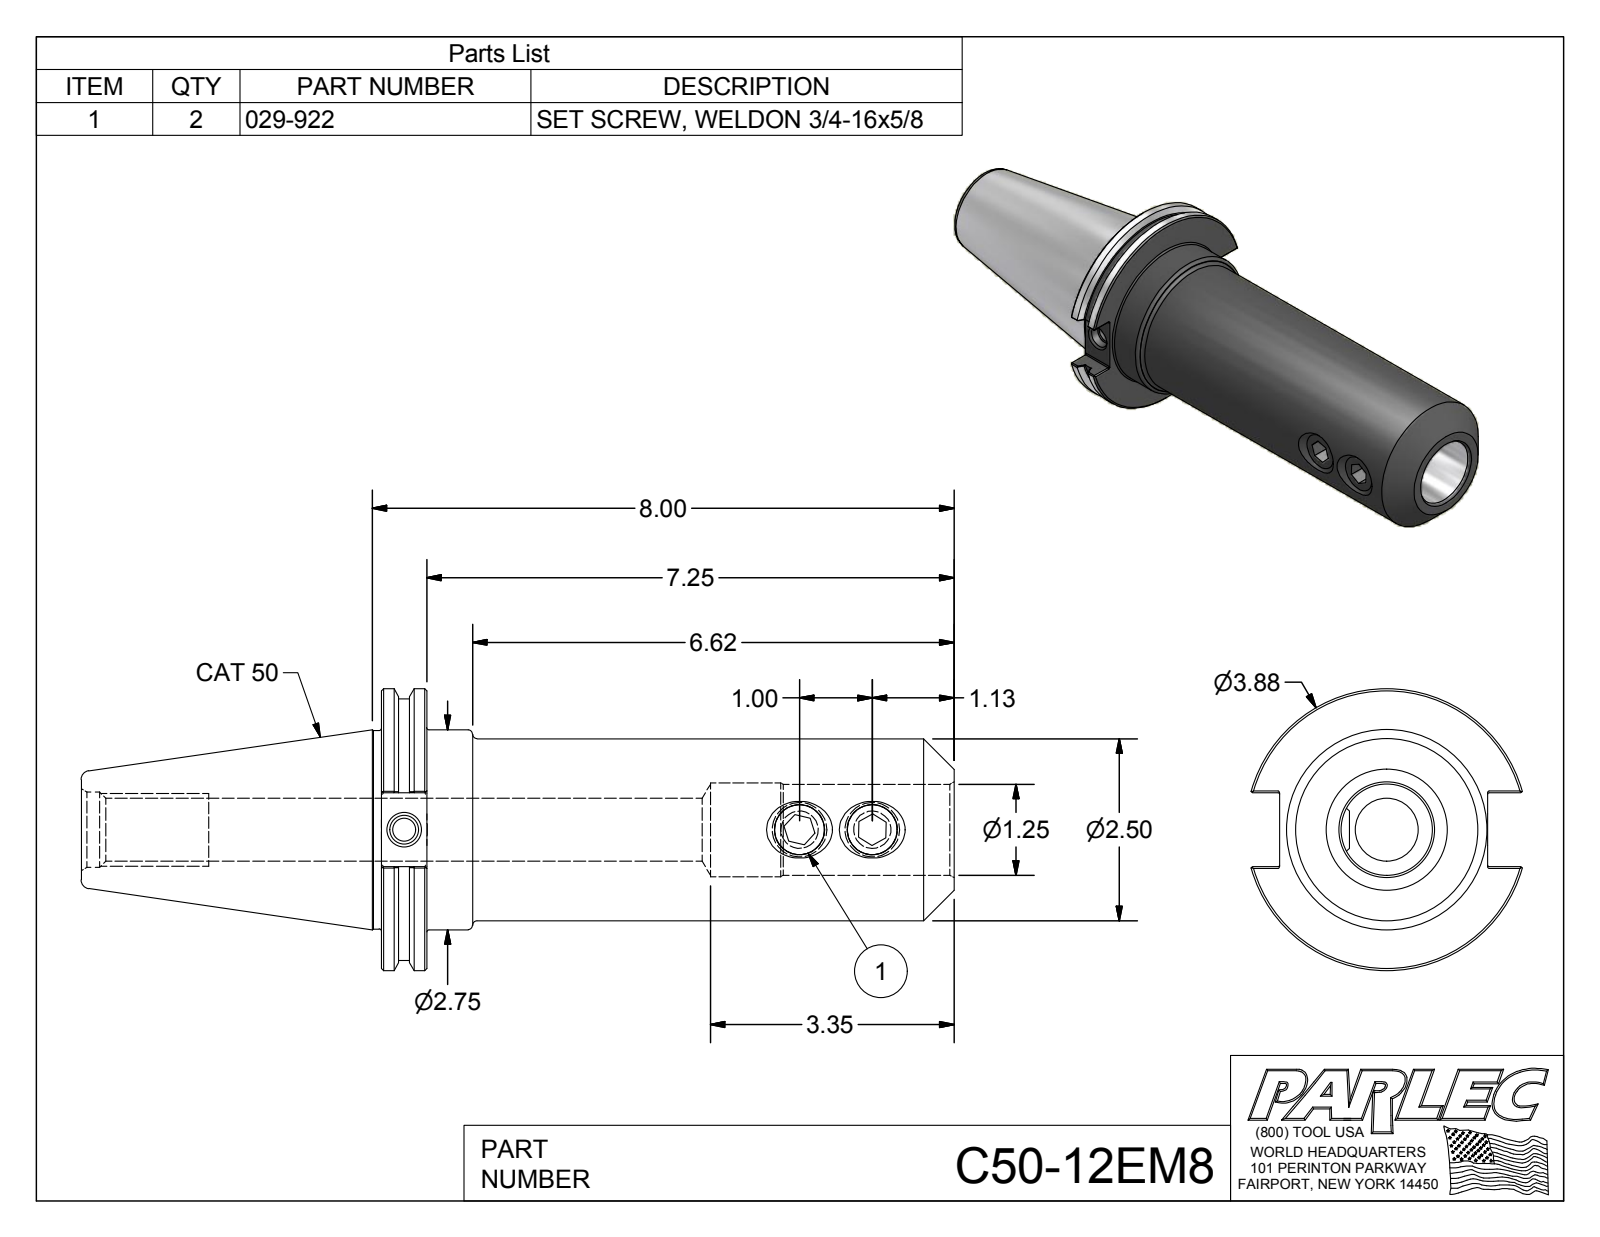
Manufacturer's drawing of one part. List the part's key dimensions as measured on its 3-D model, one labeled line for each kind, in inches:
Part name (STEP PRODUCT): C50-12EM8; C50-12EM8-1; 029-922
STEP written by: Autodesk Inventor 2012 (AUTOMOTIVE_DESIGN)
Units: inches
Bodies: 3 solids, 119 faces (51 planar, 31 cylindrical, 37 other)
Overall size (bounding box): 12 × 3.875 × 3.729
Volume: 48.42 in³ · Surface area: 152.7 in²
Round holes (diameter × count): ⌀0.682 ×2, ⌀0.315 ×1, ⌀0.399 ×1, ⌀0.865 ×1, ⌀1.038 ×1, ⌀1.25 ×1, ⌀1.29 ×1
Round bosses / shafts (diameter × count): ⌀0.75 ×2, ⌀3.875 ×1, ⌀3.594 ×1, ⌀2.75 ×1, ⌀2.73 ×1, ⌀2.5 ×1
Partial cylindrical surfaces — rounded edges, fillets, slot ends (radius × count): R0.02 ×12
Main face-to-face distances: 0.625, 7.875, 7.25, 2.526, 4.125, 4.75, 12, 0.375, 2.86, 0.333
Hole centre spacings: 1, 5.435, 6.435
